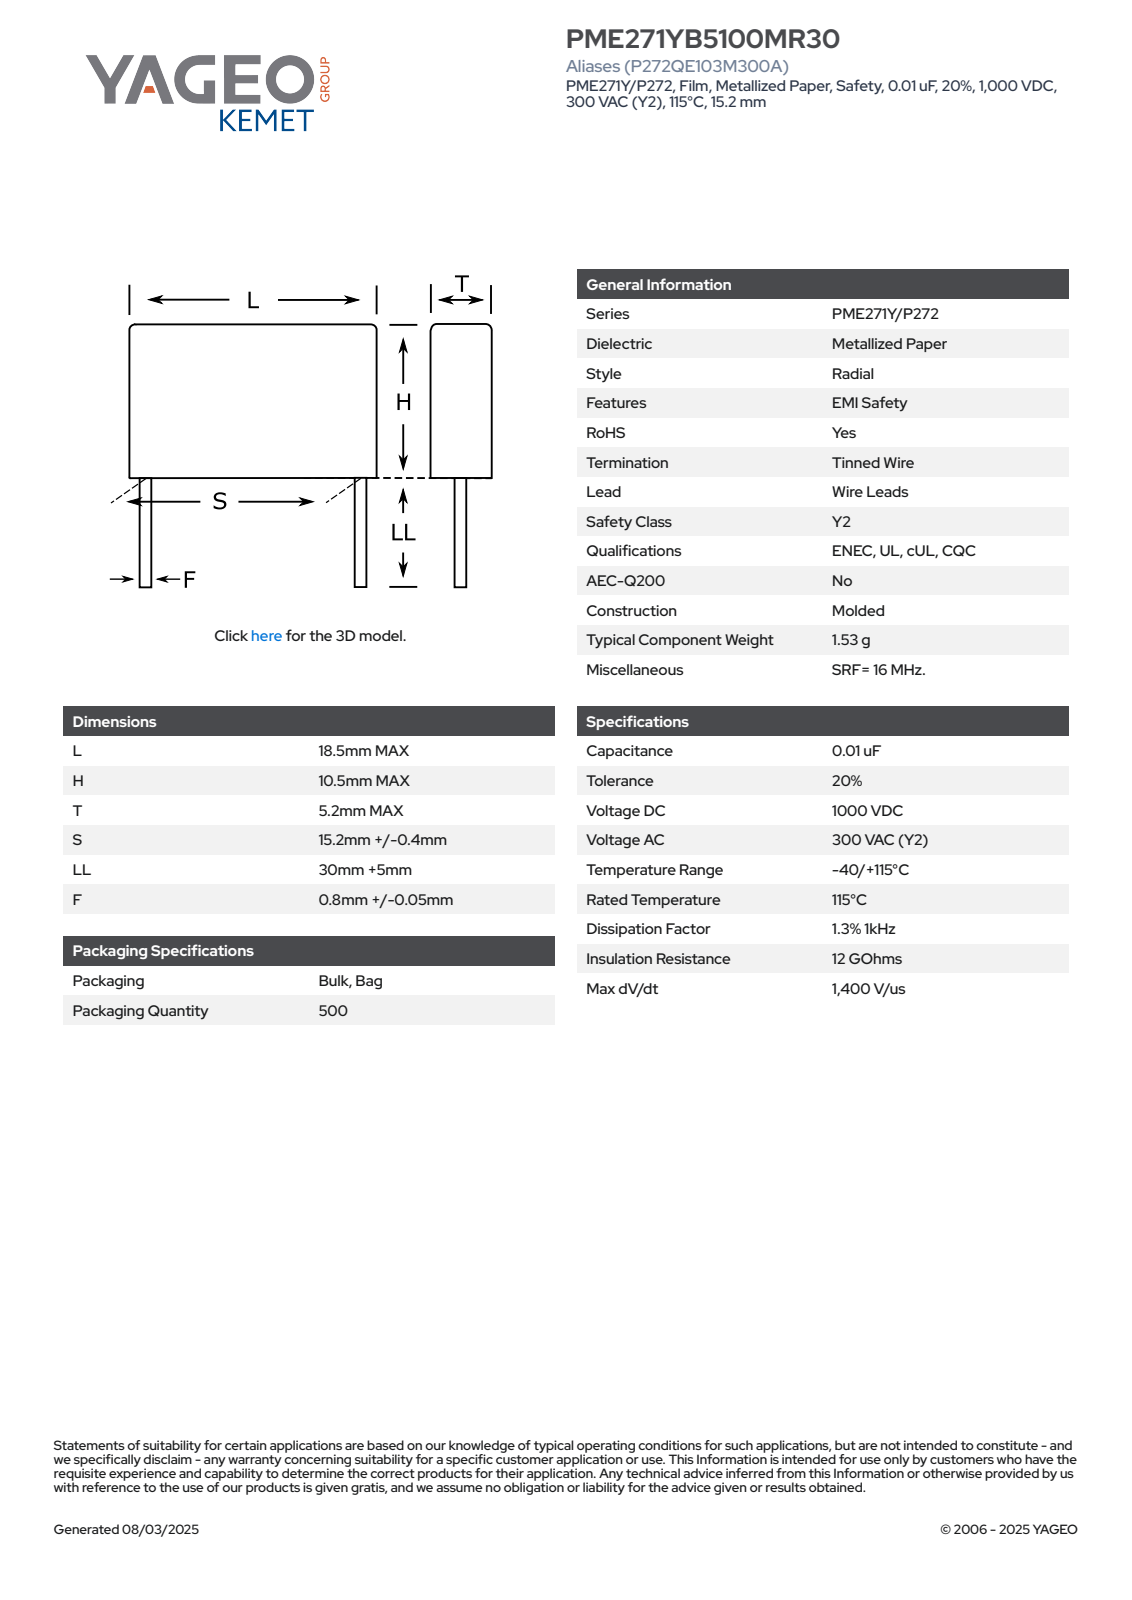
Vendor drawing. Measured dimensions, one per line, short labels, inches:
name: CFR_MOLDED_18.5X10.5X5.2_L18.5H10.5T5.2S15.2LL35F0.85
written by: SolidWorks 2014 (AUTOMOTIVE_DESIGN)
unit: in
bodies: 4 solids, 73 faces (65 planar, 8 cylindrical, 0 other)
size: 1.791 × 0.728 × 0.205
volume: 0.064 in³; area: 1.37 in²
bosses: 2× ⌀0.033
rounds: 4× R0.02
face distances: 0.205, 0.413, 0.728, 1.378, 1.791, 1.617, 0.239, 0.175, 1.551, 0.173
